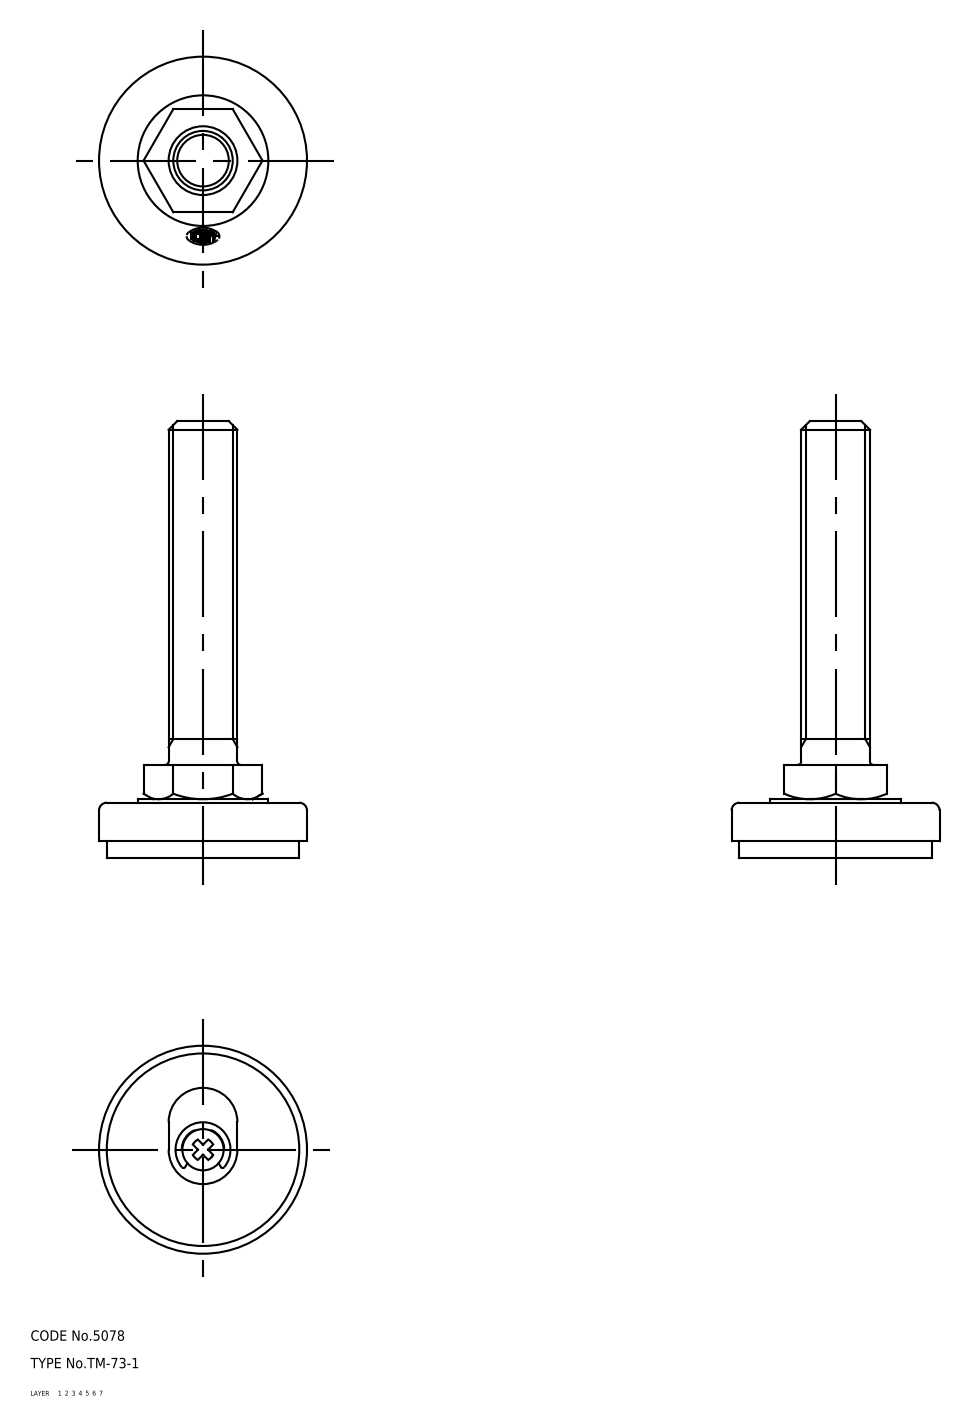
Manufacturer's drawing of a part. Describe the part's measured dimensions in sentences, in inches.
The part is named "washer; rubber pad; retainer; cover (+3 more)". Its 3-D file was written by "CADfix (AUTOMOTIVE_DESIGN)". It is 6 solids with 111 faces: 0 planar, 0 cylindrical and 111 other. Overall it measures 5 by 2.382 by 2.382 inches. Its volume is 4.924 cubic inches and its surface area 54.39 square inches.
